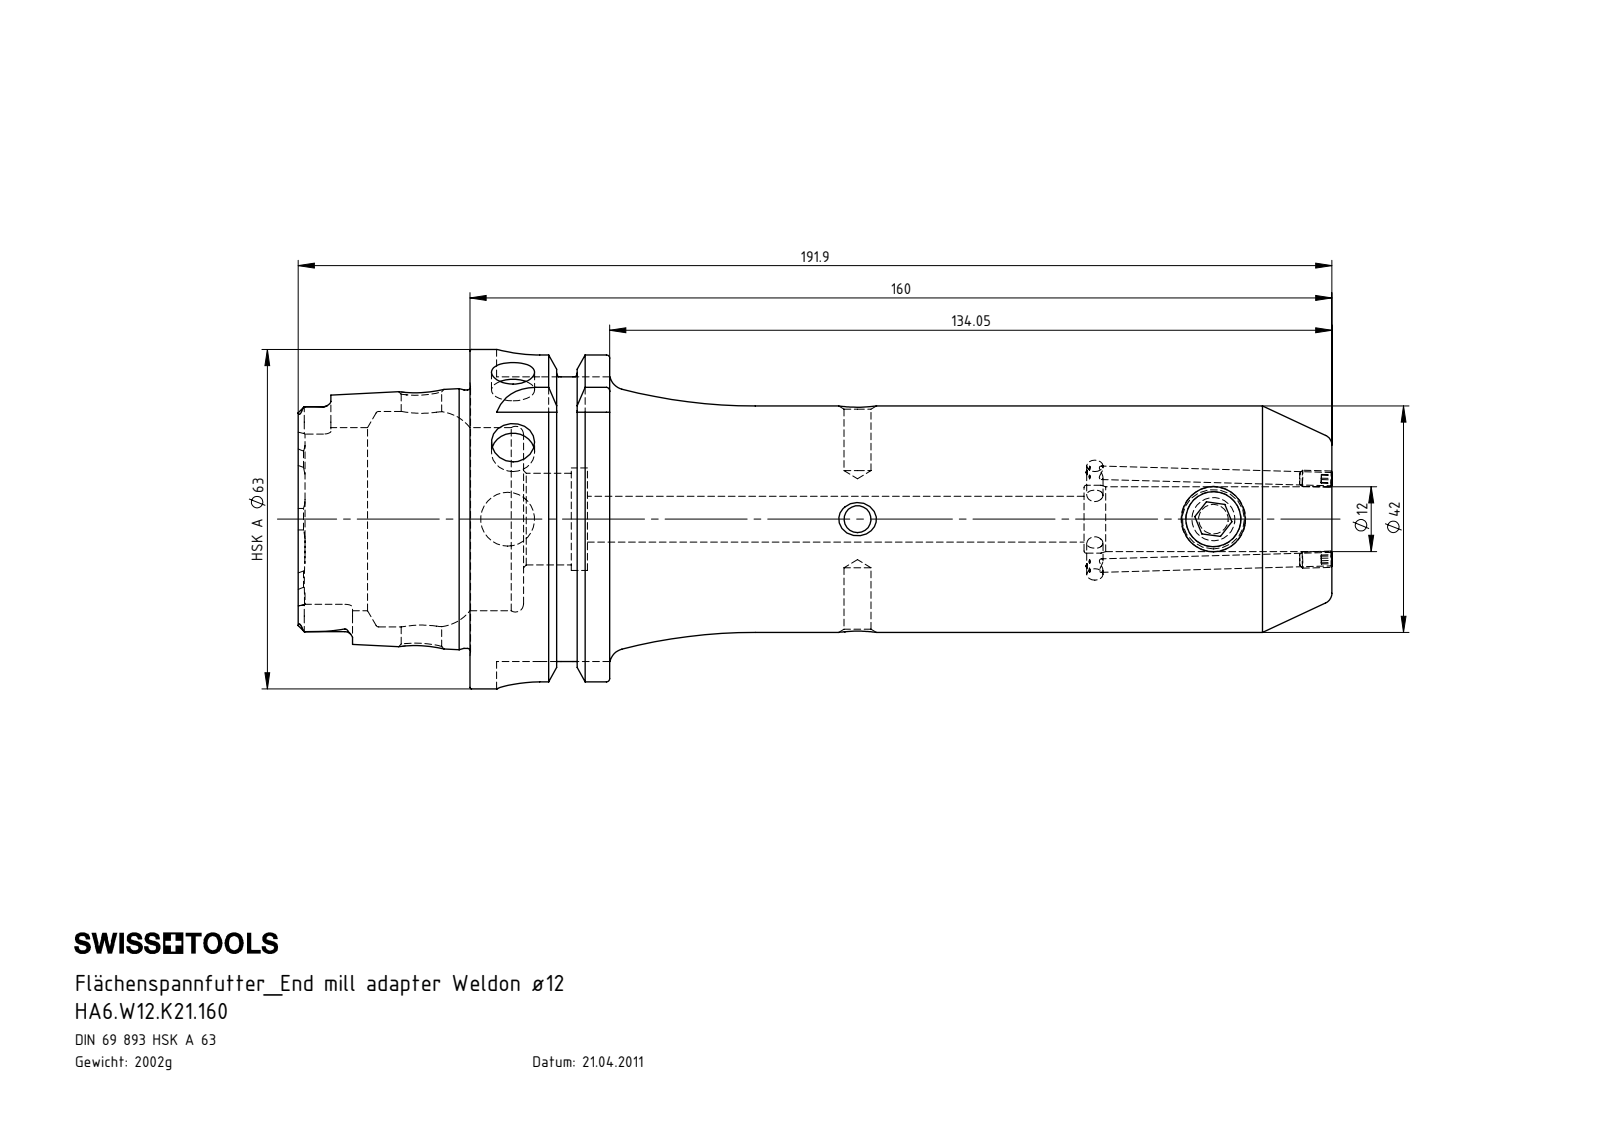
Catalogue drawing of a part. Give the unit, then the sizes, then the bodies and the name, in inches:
Units: inches
Overall size (bounding box): 7.558 × 2.48 × 2.48
Round holes (diameter × count): ⌀0.098 ×2, ⌀0.197 ×2, ⌀0.315 ×2, ⌀0.118 ×1, ⌀0.295 ×1, ⌀0.335 ×1, ⌀0.394 ×1, ⌀0.404 ×1, ⌀0.472 ×1, ⌀0.496 ×1, ⌀0.669 ×1, ⌀0.748 ×1
Round bosses / shafts (diameter × count): ⌀0.118 ×2, ⌀2.48 ×1, ⌀2.163 ×1, ⌀1.887 ×1, ⌀1.654 ×1, ⌀0.472 ×1
Partial cylindrical surfaces — rounded edges, fillets, slot ends (radius × count): R0.055 ×6, R0.113 ×4, R0.315 ×4
Main face-to-face distances: 1.022, 0.63, 0.392, 6.299, 5.907, 5.278, 1.256, 1.648, 2.278, 7.555
Hole centre spacings: 2.557, 2.6, 3.187, 5.157
Volume: 15.56 in³ · Surface area: 71.35 in²
Bodies: 4 solids, 289 faces (78 planar, 81 cylindrical, 130 other)
Part name (STEP PRODUCT): HA6.W12.K21.160; ERU-CJ2.001.006; W12-ER1.001.016; HA6-W12.K21.160_C_Fertigbearbeitung
STEP written by: SolidWorks 2012 (CONFIG_CONTROL_DESIGN)
